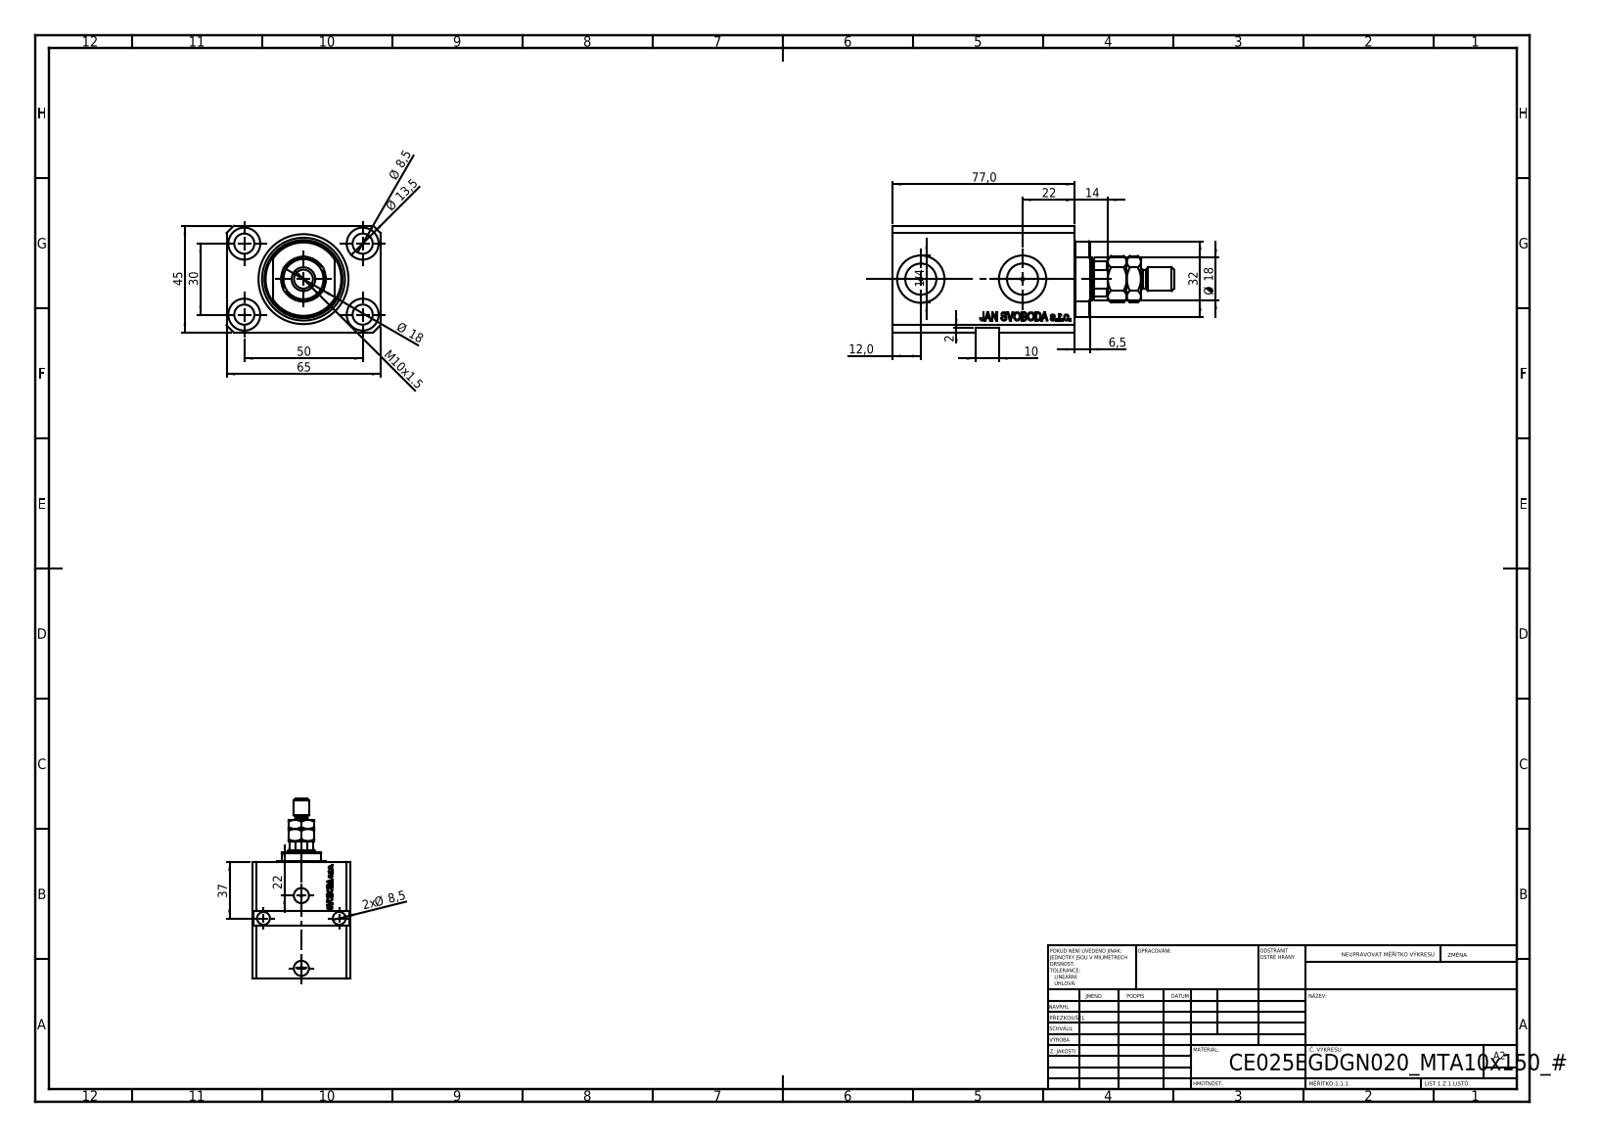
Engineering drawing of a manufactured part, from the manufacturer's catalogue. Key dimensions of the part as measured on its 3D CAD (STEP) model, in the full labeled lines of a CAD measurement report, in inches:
Part name (STEP PRODUCT): MTA; V250CE_C_VCP; V250CE_VC_E; V250CE_E_Body
STEP written by: SolidWorks 2019 (CONFIG_CONTROL_DESIGN)
Units: inches
Bodies: 4 solids, 962 faces (454 planar, 100 cylindrical, 408 other)
Overall size (bounding box): 4.685 × 2.559 × 1.772
Volume: 11.75 in³ · Surface area: 85.46 in²
Round holes (diameter × count): ⌀0.335 ×7, ⌀0.049 ×4, ⌀0.531 ×4, ⌀0.394 ×2, ⌀0.518 ×2, ⌀0.787 ×2, ⌀0.709 ×1, ⌀0.984 ×1, ⌀1.496 ×1
Round bosses / shafts (diameter × count): ⌀0.394 ×1, ⌀0.315 ×1
Partial cylindrical surfaces — rounded edges, fillets, slot ends (radius × count): R0.335 ×1, R0.63 ×1
Main face-to-face distances: 1.772, 2.559, 0.551, 2.48, 3.031, 0.272, 2.209, 2.76, 1.693, 1.102
Hole centre spacings: 1.148, 1.969, 1.181, 1.613, 1.63, 2.296, 0.021, 1.693
